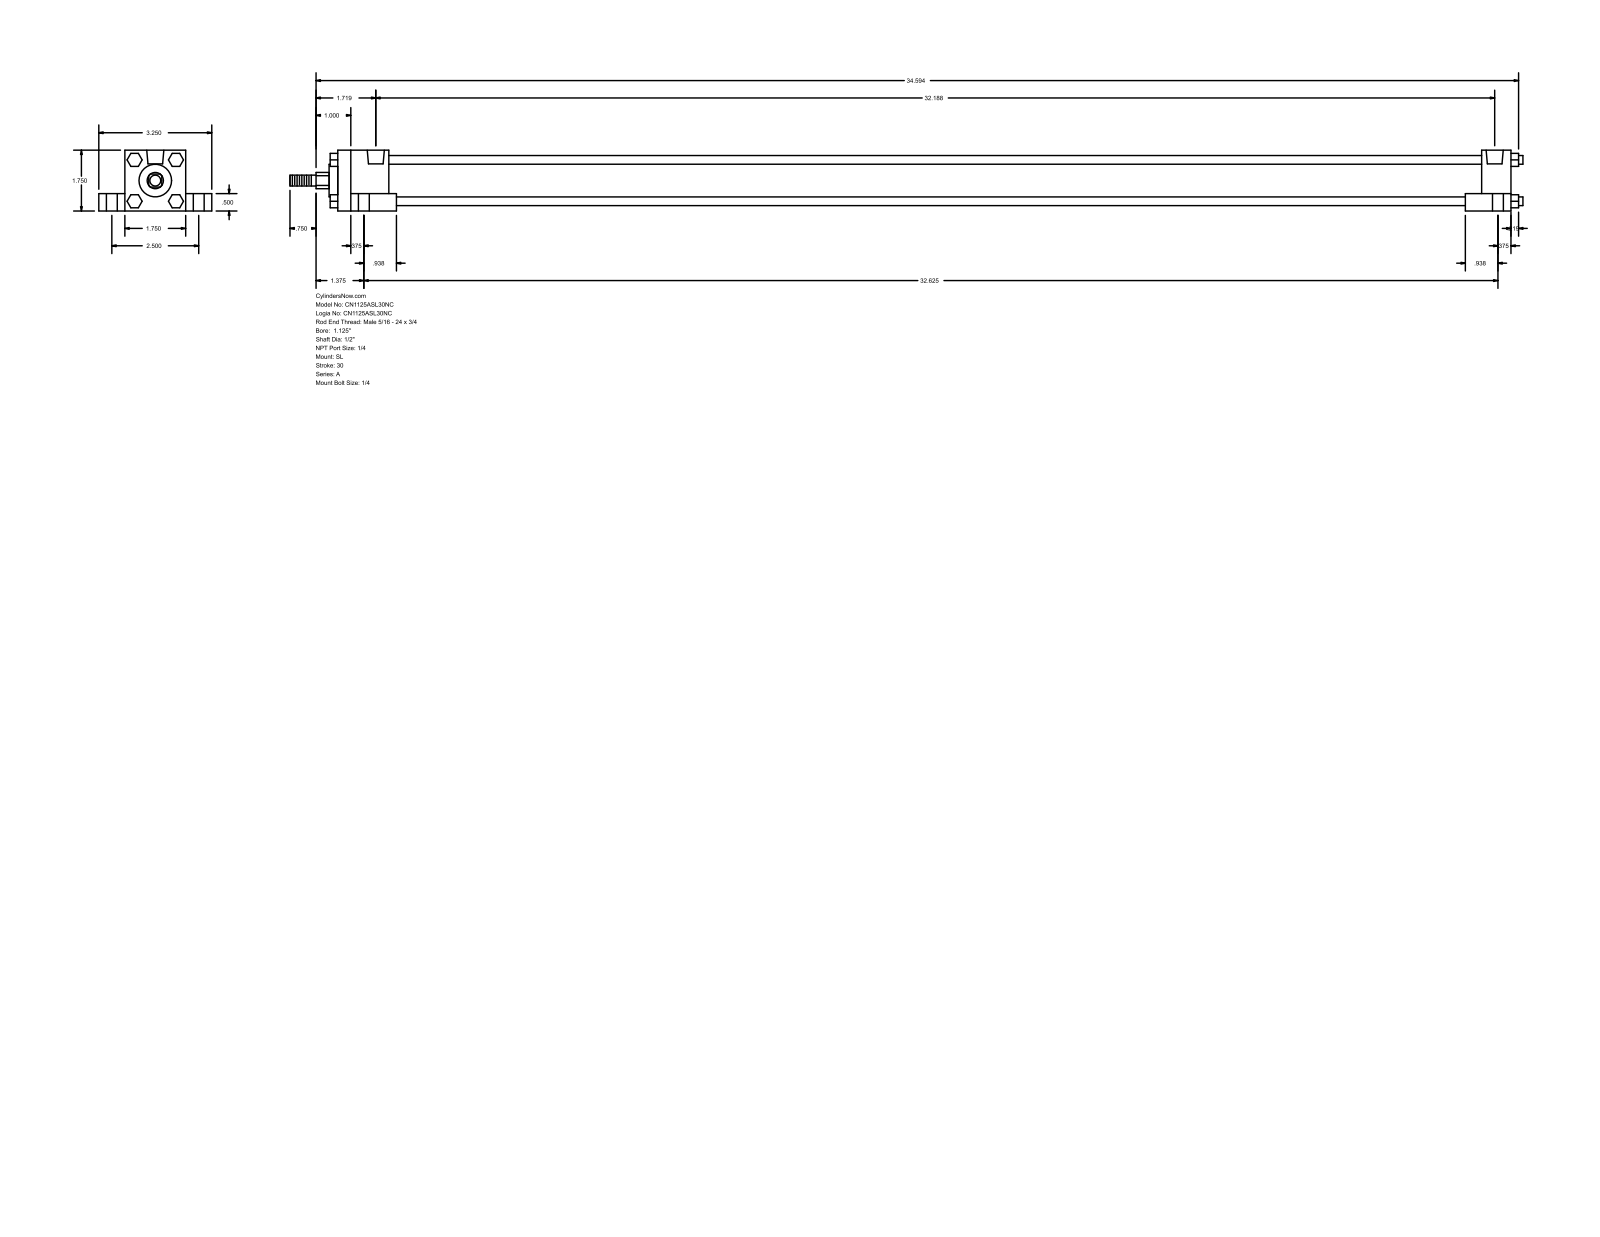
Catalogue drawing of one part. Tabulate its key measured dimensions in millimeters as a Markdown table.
| quantity | value |
| --- | --- |
| part name | A_SL__0112_0.5 |
| STEP written by | GSSL Pune (CONFIG_CONTROL_DESIGN) |
| units | millimeters |
| bodies | 0 solids, 150 faces (114 planar, 36 cylindrical, 0 other) |
| overall size | 900.91 × 82.55 × 44.45 |
| round holes (diameter × count) | 5.56 × 4, 7.94 × 4, 14.29 × 4, 12.49 × 2 |
| round bosses / shafts (diameter × count) | 6.35 × 4, 31.88 × 1, 23.81 × 1, 12.7 × 1, 7.94 × 1 |
| partial cylindrical surfaces (radius × count) | 5.94 × 1 |
| main face-to-face distances | 44.46, 31.76, 12.7, 19.04, 63.5, 819.94, 857.24, 835.81, 21.43, 37.3 |
| hole center spacings | 31.84, 32, 32.93, 33.39, 63.5, 814.39, 818.98, 820.55 |
